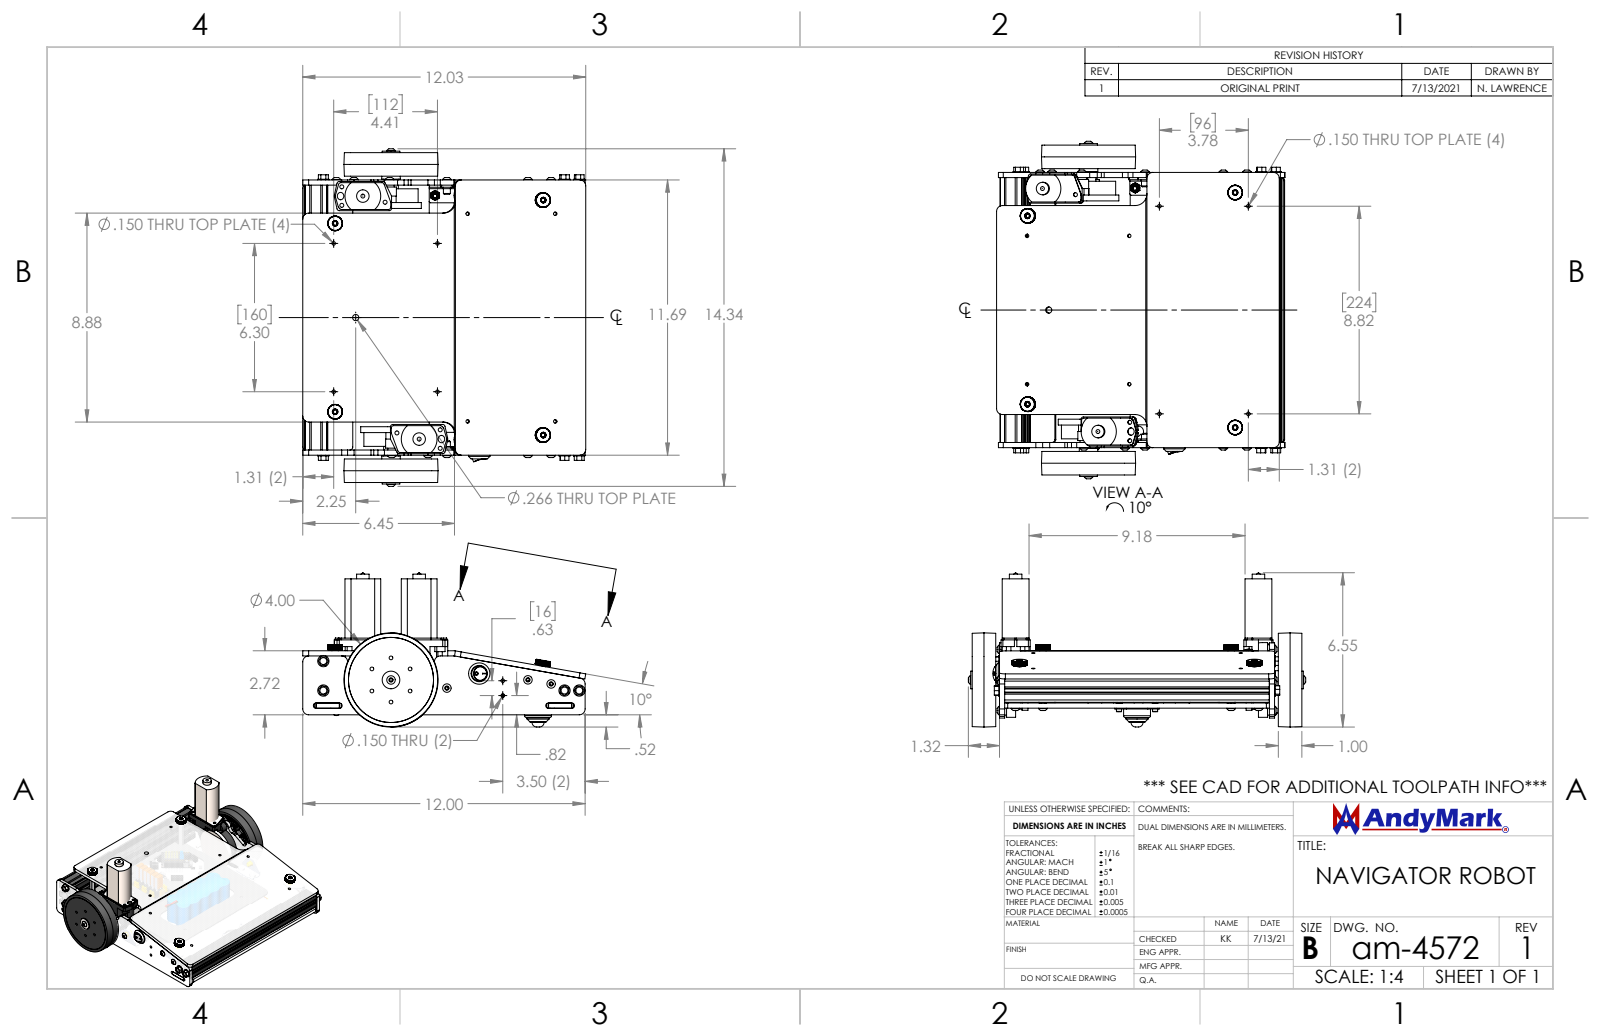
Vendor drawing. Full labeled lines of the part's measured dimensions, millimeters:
Part name (STEP PRODUCT): Rubber Bumper; AM-2235a Hex Snow Blower Motor; ESP32 Control Panel; Power and Motor Wires (+8 more)
STEP written by: SolidWorks 2021 (AUTOMOTIVE_DESIGN)
Units: millimetres
Bodies: 256 solids, 15794 faces (10876 planar, 3195 cylindrical, 1723 other)
Overall size (bounding box): 364.16 × 305.48 × 166.48
Volume: 1 979 000 mm³ · Surface area: 1 046 000 mm²
Round holes (diameter × count): ⌀0.8 ×260, ⌀0.5 ×100, ⌀0.9 ×83, ⌀1.27 ×51, ⌀2 ×36, ⌀4.18 ×32, ⌀1.02 ×28, ⌀4.04 ×20, ⌀5.11 ×19, ⌀2.87 ×15, ⌀3 ×15, ⌀2.59 ×12
Round bosses / shafts (diameter × count): ⌀9.17 ×18, ⌀4.83 ×16, ⌀2.8 ×12, ⌀6.35 ×10, ⌀9.91 ×6, ⌀3 ×5, ⌀15.87 ×4, ⌀14.61 ×4
Partial cylindrical surfaces — rounded edges, fillets, slot ends (radius × count): R7.94 ×285, R0.25 ×206, R0.5 ×90, R0.25 ×76, R0.1 ×61, R0.2 ×43, R0.4 ×42, R1 ×32
Main face-to-face distances: 5.59, 5.58, 11.57, 39.17, 17.15, 56.32, 50.74, 61.91, 56.33, 44.76
Hole centre spacings: 23.81, 25.4, 23.82, 25.41, 253.49, 0.38, 33.03, 41.24
